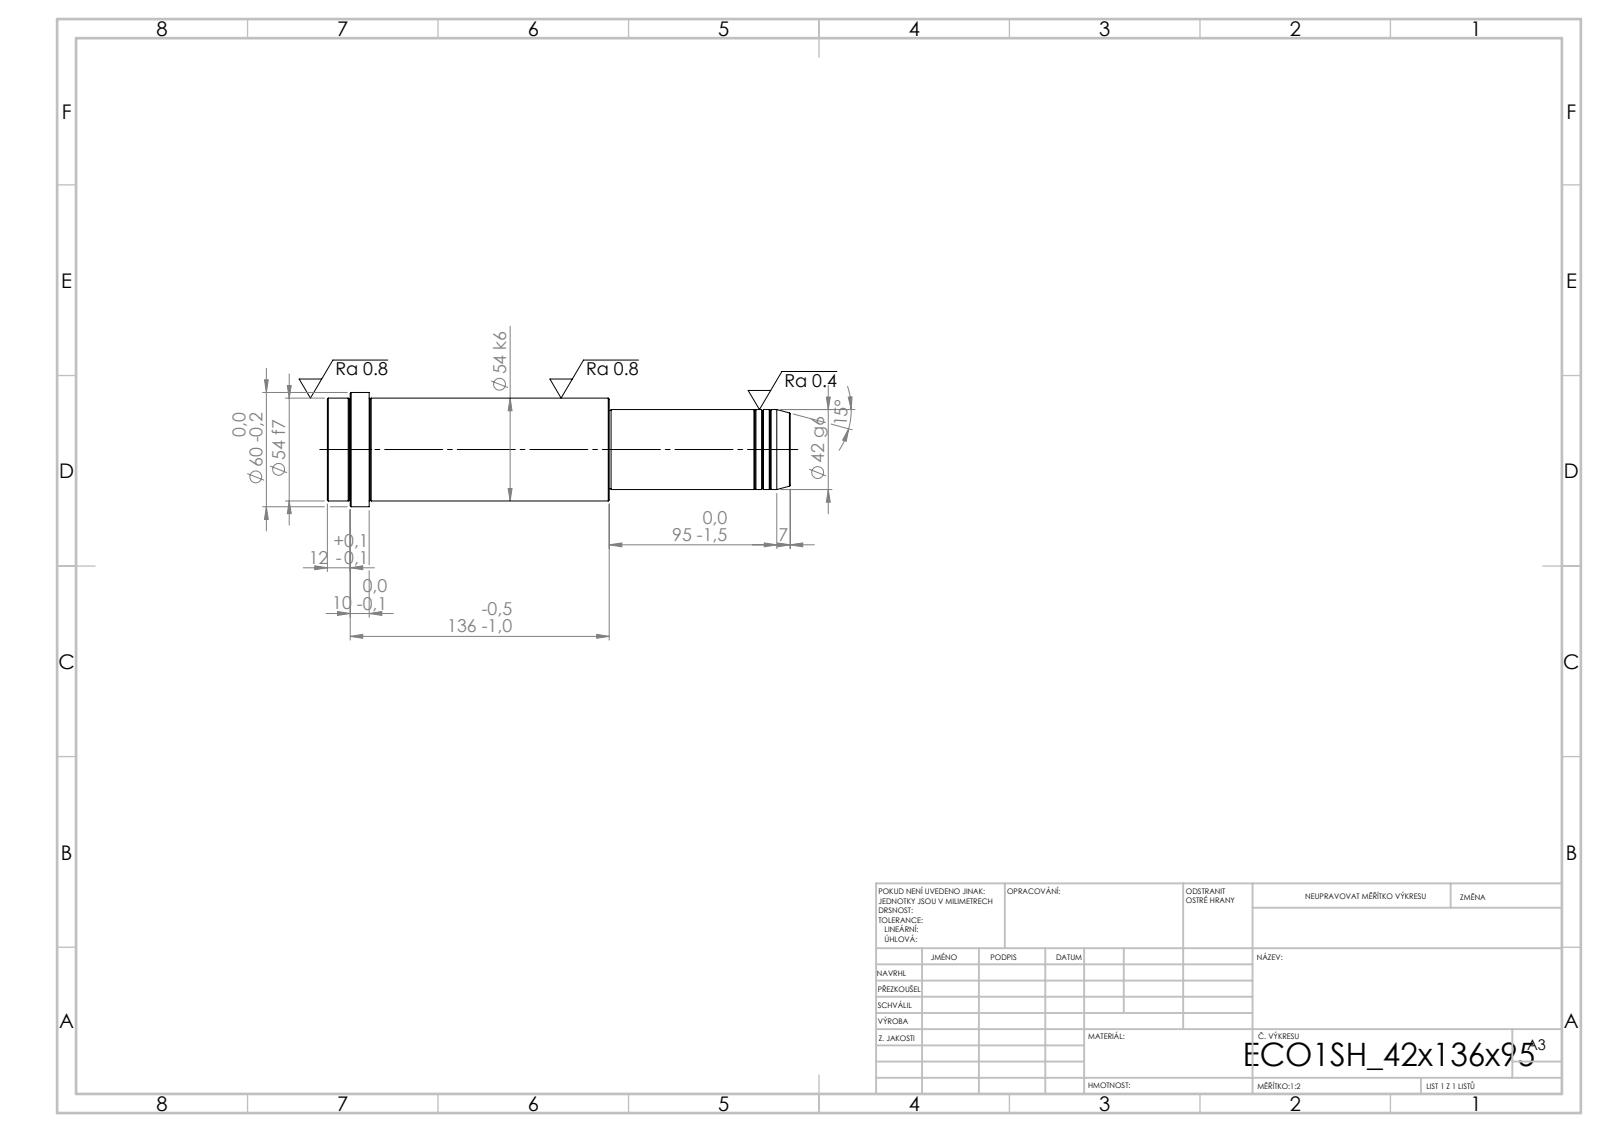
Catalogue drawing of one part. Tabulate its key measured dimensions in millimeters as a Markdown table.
| quantity | value |
| --- | --- |
| STEP written by | SolidWorks 2019 (CONFIG_CONTROL_DESIGN) |
| units | millimeters |
| bodies | 1 solid, 52 faces (6 planar, 16 cylindrical, 30 other) |
| overall size | 243 × 60 × 60 |
| volume | 474 681 mm³ |
| surface area | 43 601 mm² |
| round bosses / shafts (diameter × count) | 60 × 1, 54 × 1, 42 × 1, 41 × 1 |
| main face-to-face distances | 243, 95, 148, 221, 126, 22, 231, 136, 10, 12 |
